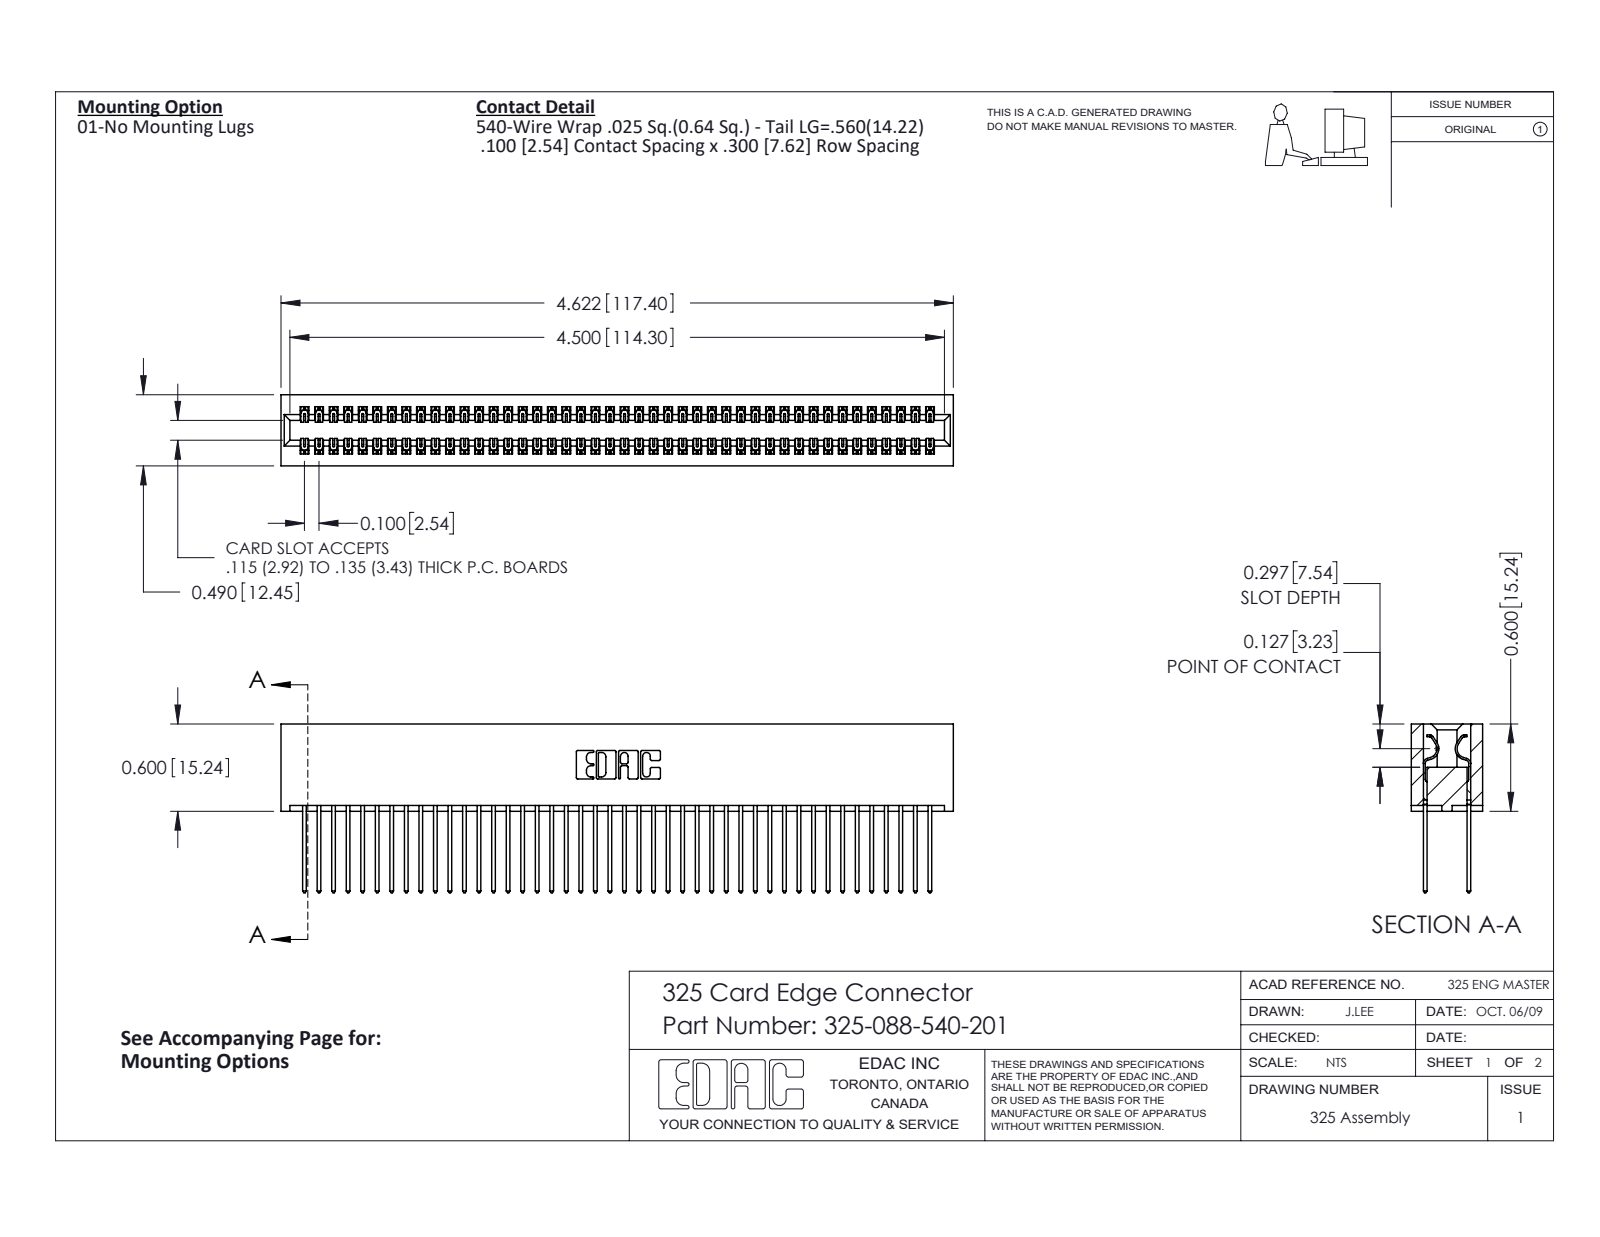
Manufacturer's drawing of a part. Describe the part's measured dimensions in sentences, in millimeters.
The part is named "325 Part_Lugless; 325-088-540-201; 325-292-001_325-293-140". Its 3-D file was written by "SolidWorks 2016 (CONFIG_CONTROL_DESIGN)". It is 89 solids with 4682 faces: 3234 planar, 1448 cylindrical and 0 other. Overall it measures 117.4 by 29.5 by 12.4 millimeters. Its volume is 16 100 cubic millimeters and its surface area 21 800 square millimeters. Partial cylindrical surfaces (rounded edges, fillets, slot ends): 132 of radius 0.2, 88 of radius 0.3, 22 of radius 0.3, 6 of radius 0.2, 6 of radius 0.8, 3 of radius 0.7, 2 of radius 0.4, 2 of radius 0.6. The main face-to-face distances are 2.1, 10.3, 7.6, 2.7, 9.7, 0.6, 8.3, 12.4, 7, 14.2.
